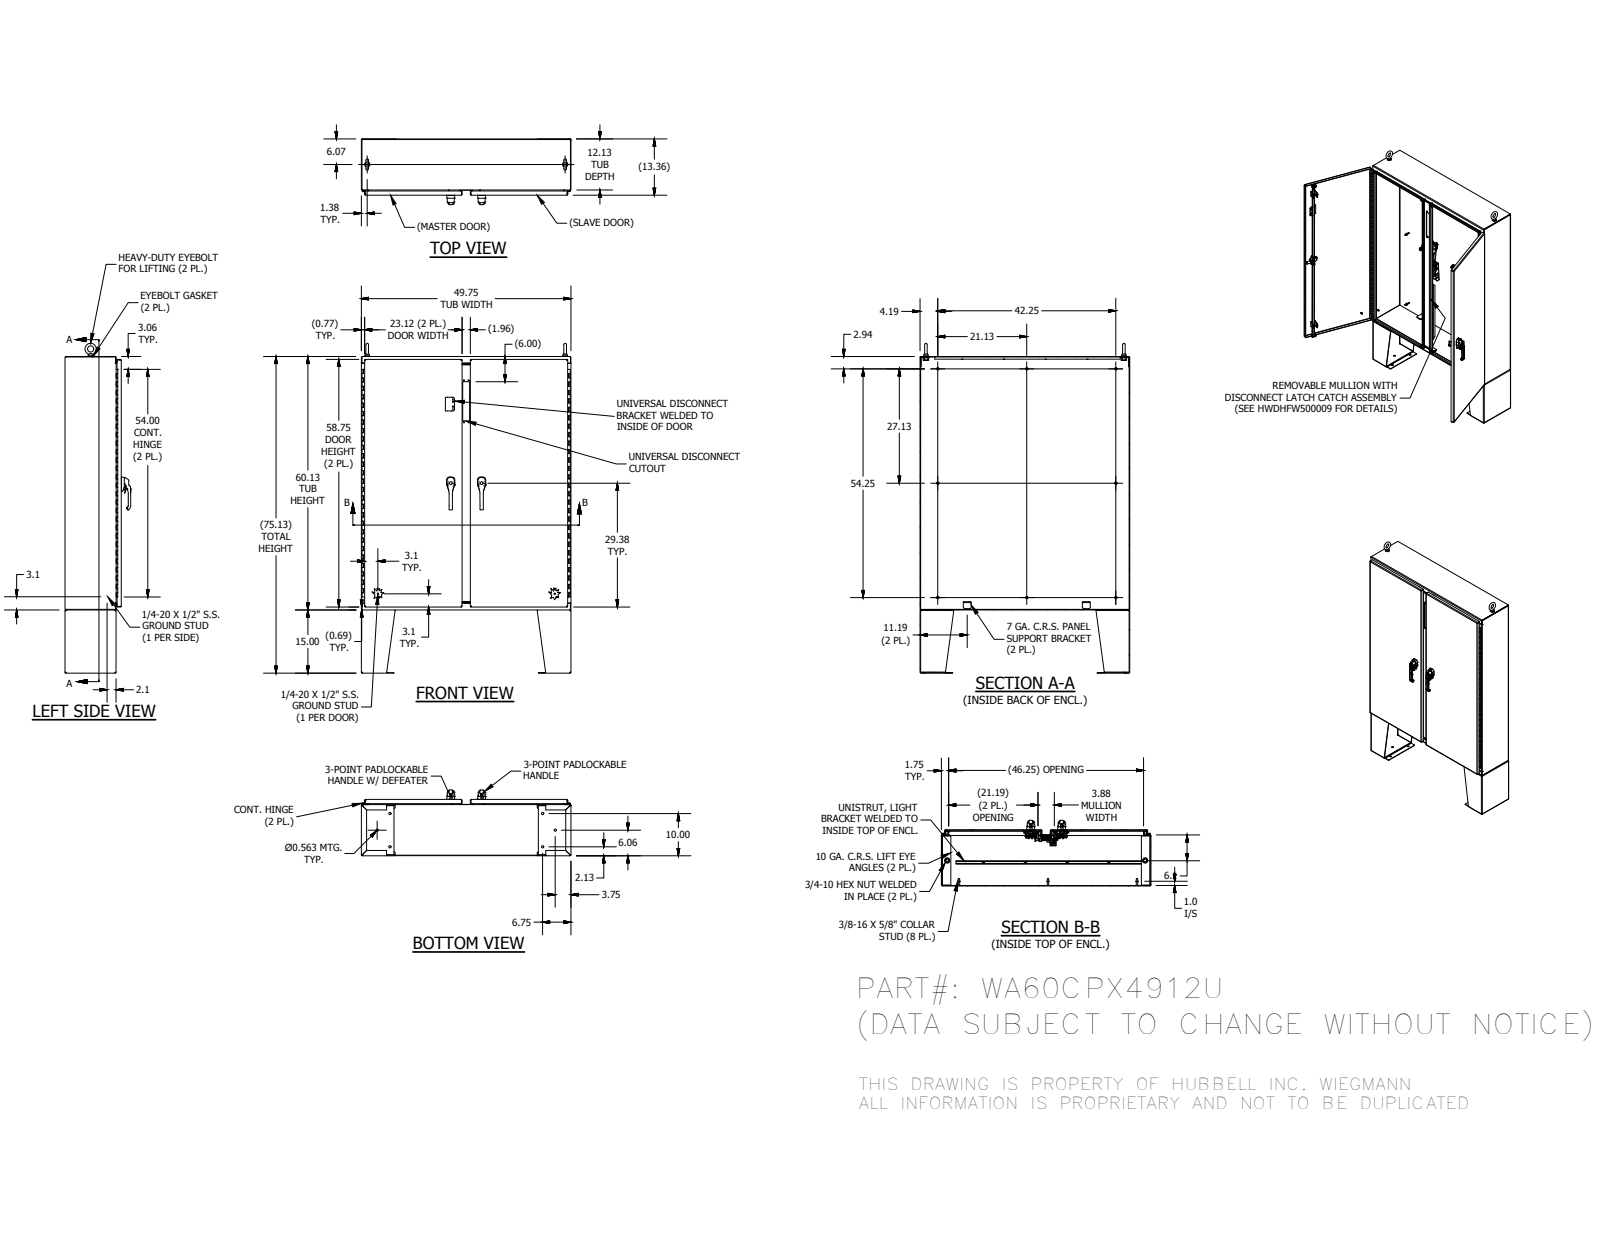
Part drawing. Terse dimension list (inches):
name: WA60CPX4912UBLR; WACPX4912UTOP; WACPX4912UBTM; 30364 (+8 more)
written by: Autodesk Inventor 2016 (AUTOMOTIVE_DESIGN)
unit: in
bodies: 207 solids, 8461 faces (3907 planar, 2837 cylindrical, 1717 other)
size: 78.248 × 49.75 × 15.608
volume: 1 519 in³; area: 23 750 in²
holes: 21× ⌀0.25, 18× ⌀0.375, 18× ⌀0.563, 8× ⌀0.2, 8× ⌀0.203, 8× ⌀0.276, 8× ⌀0.313, 6× ⌀0.156, 6× ⌀0.19, 6× ⌀0.196, 6× ⌀0.201, 6× ⌀0.213
bosses: 18× ⌀0.25, 16× ⌀0.33, 14× ⌀0.625, 9× ⌀0.563, 9× ⌀0.375, 9× ⌀0.337, 8× ⌀1, 8× ⌀0.438
rounds: 344× R0.02, 202× R0.012, 144× R0.02, 42× R0.019, 40× R0.05, 40× R0.125, 37× R0.094, 27× R0.079
face distances: 0.134, 13.217, 13.083, 13.35, 0.134, 49.616, 59.991, 0.125, 11.991, 49.482
hole spacings: 1.102, 7.334, 2.759, 7.387, 0.886, 1.142, 1.195, 1.271
